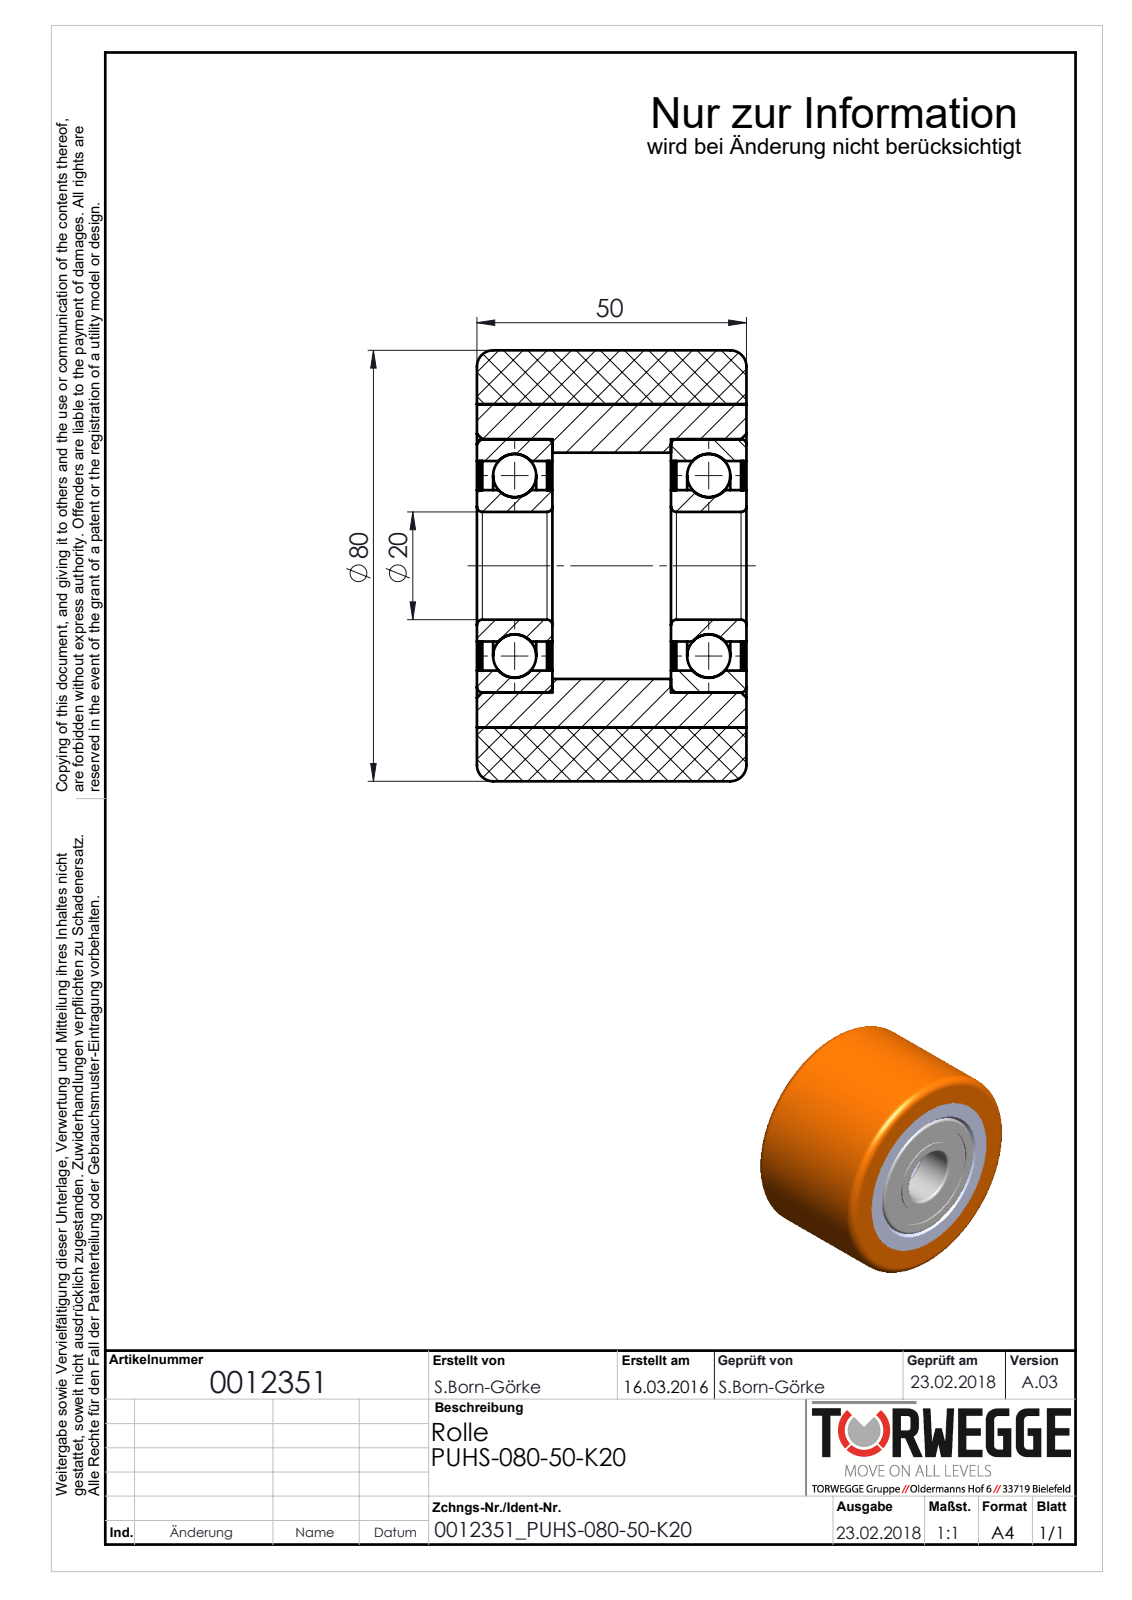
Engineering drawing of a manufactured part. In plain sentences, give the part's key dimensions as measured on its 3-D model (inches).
The part is named "0012351_PUHS-080-50-K20". Its 3-D file was written by "SolidWorks 2016 (AUTOMOTIVE_DESIGN)". It is 12 solids with 118 faces: 22 planar, 52 cylindrical and 44 other. Overall it measures 3.15 by 3.15 by 1.969 inches. Its volume is 12.45 cubic inches and its surface area 109 square inches. Round holes: 1 of diameter 0.787, 1 of diameter 1.106, 1 of diameter 1.531, 1 of diameter 1.654, 1 of diameter 1.85, 1 of diameter 2.362. Round bosses or shafts: 1 of diameter 3.15. The main face-to-face distances are 0.02, 1.417, 0.512, 1.969, 0.039, 0.531, 1.437, 0.492, 1.398, 0.551.
